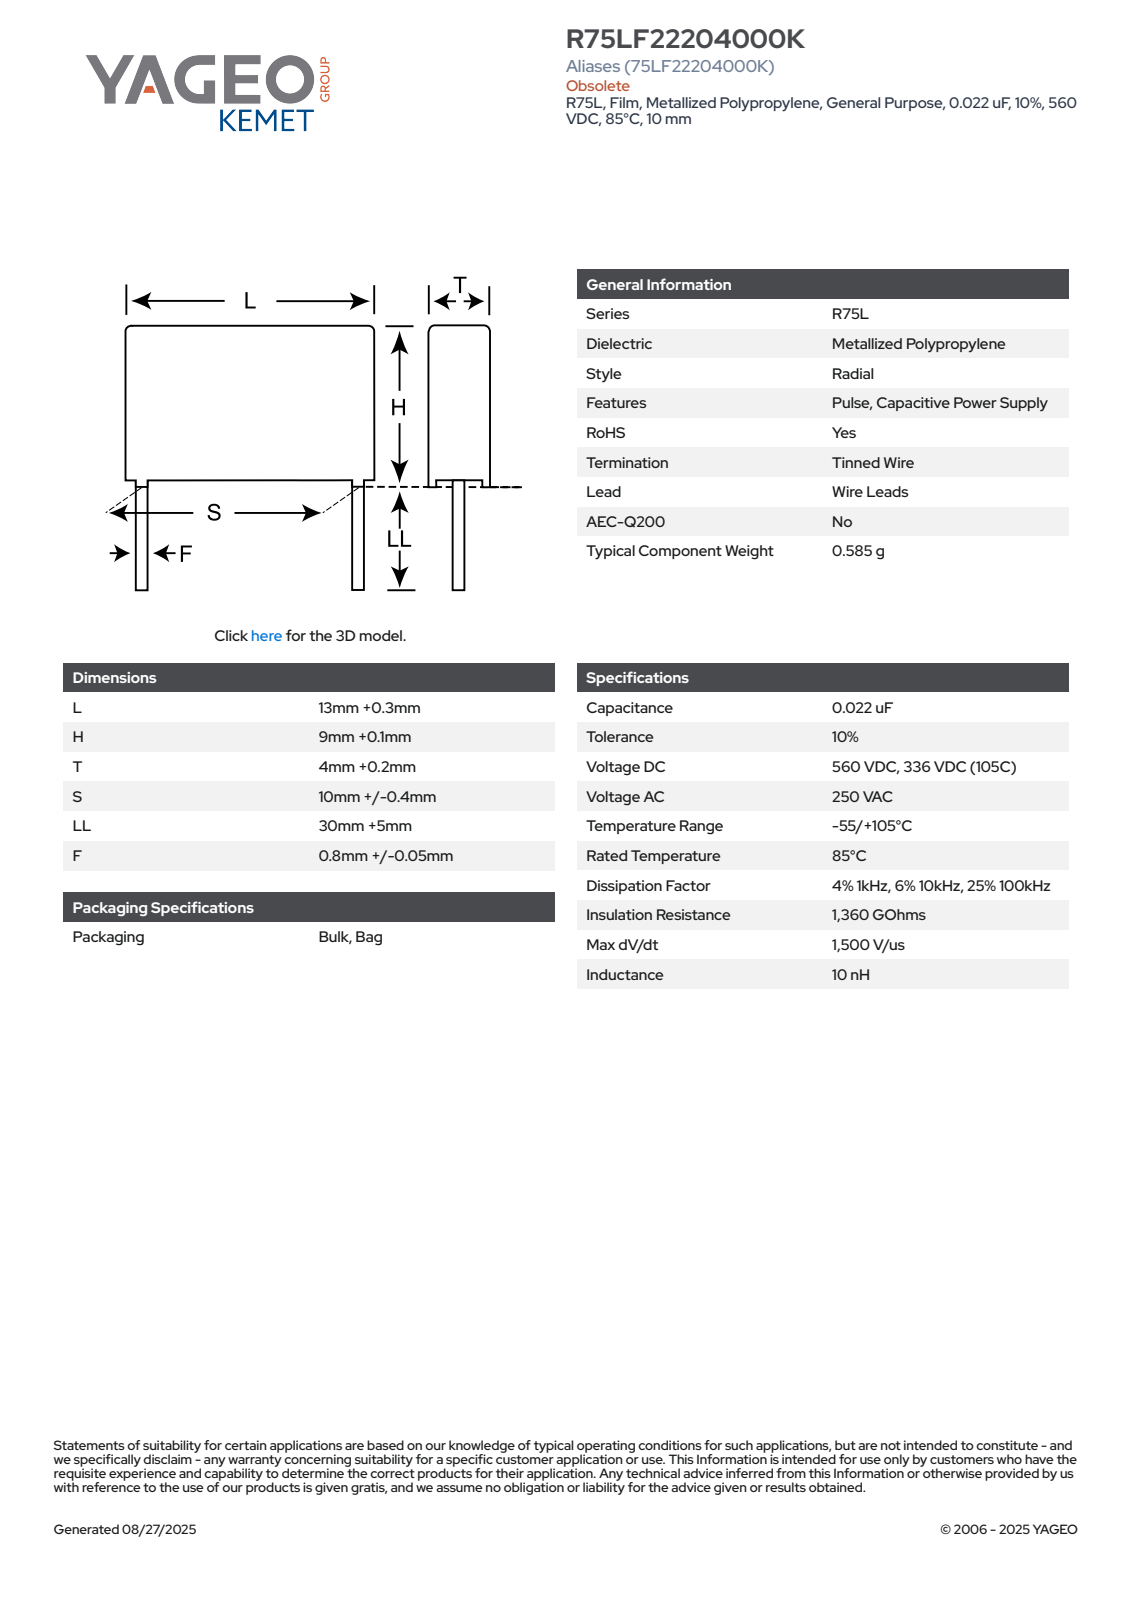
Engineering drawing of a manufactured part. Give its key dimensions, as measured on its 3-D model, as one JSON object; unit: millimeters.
{"part_name": "CFR_RB3_13X9X4_L13.3H9.1T4.2S10LL35F0.85", "step_written_by": "SolidWorks 2014 (AUTOMOTIVE_DESIGN)", "units": "millimeters", "bodies": {"solids": 4, "faces": 85, "planar": 77, "cylindrical": 8, "other": 0}, "overall_size": [44.1, 13.3, 4.21], "volume_mm3": 514, "surface_area_mm2": 642, "round_bosses_or_shafts": [[0.85, 2]], "partial_cylinders_radius": [[0.5, 4]], "face_to_face_distances": [4.2, 8.35, 13.3, 0.44, 3.76, 0.75, 9.1, 3.32, 0.31, 8.79]}
